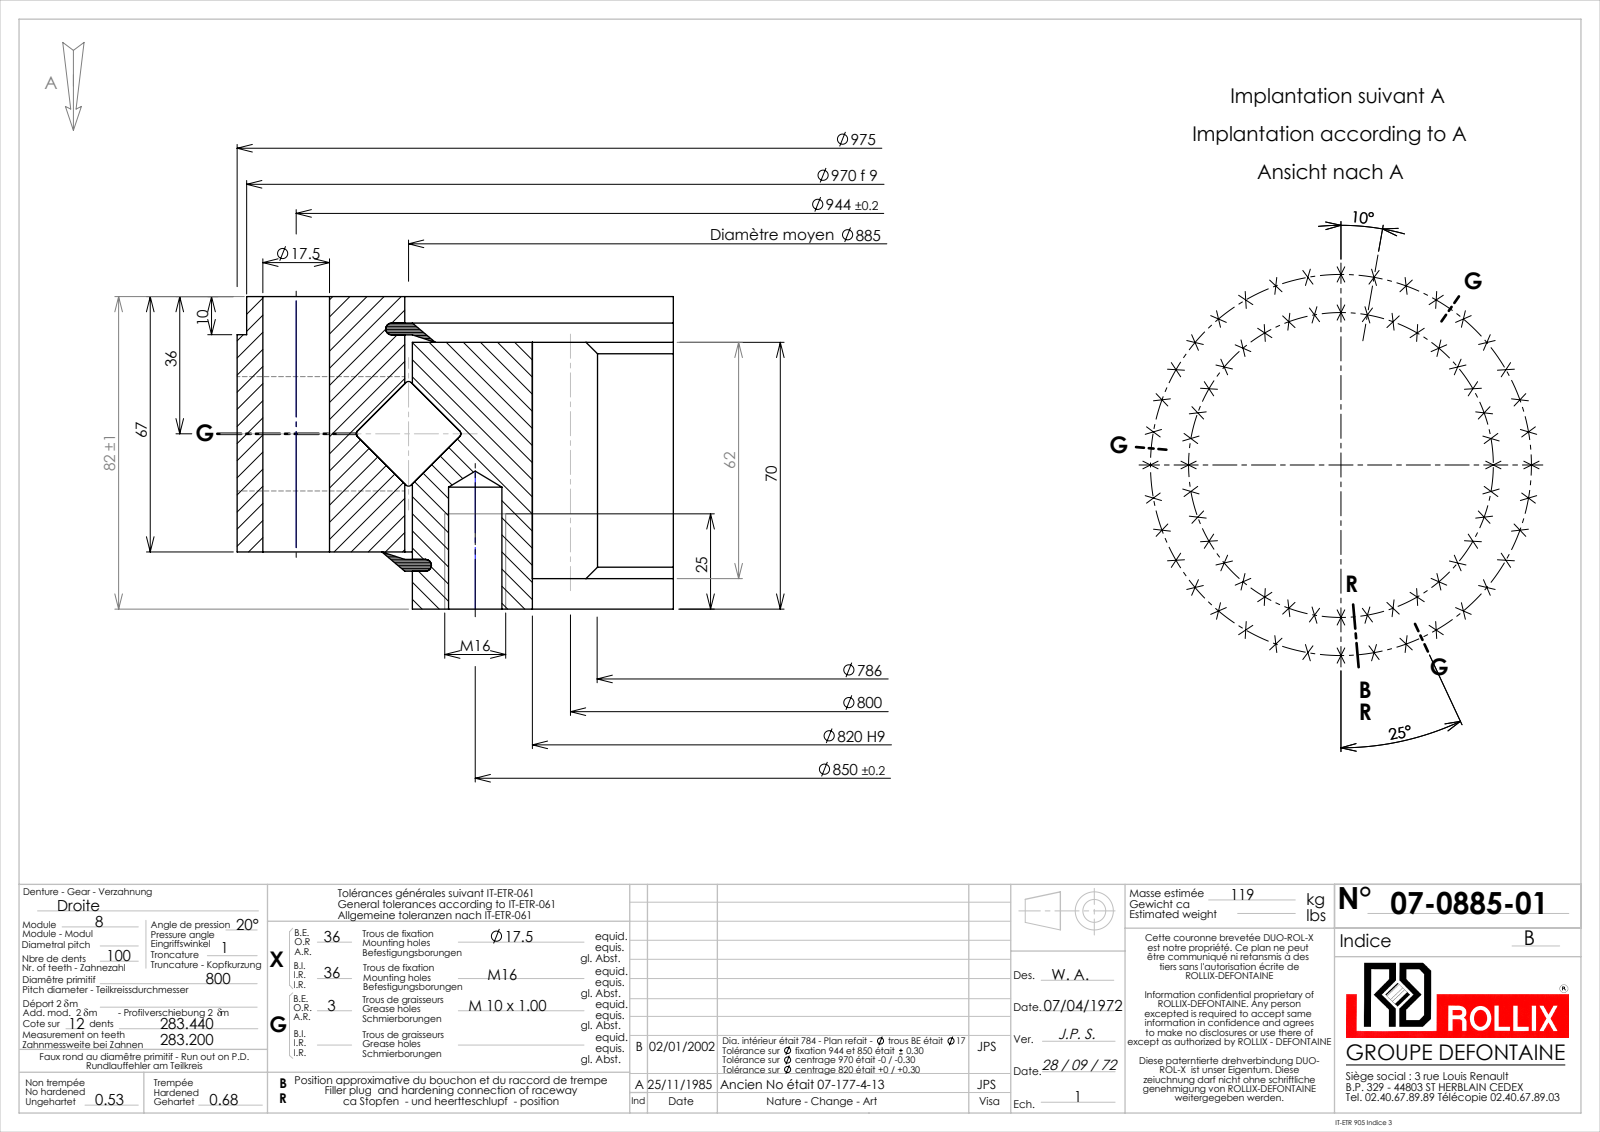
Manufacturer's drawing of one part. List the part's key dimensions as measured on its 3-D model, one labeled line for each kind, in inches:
Part name (STEP PRODUCT): 07-0885-01
STEP written by: SolidWorks 2016 (CONFIG_CONTROL_DESIGN)
Units: inches
Bodies: 5 solids, 897 faces (315 planar, 270 cylindrical, 312 other)
Overall size (bounding box): 38.386 × 38.386 × 3.228
Volume: 869.6 in³ · Surface area: 2 821 in²
Round holes (diameter × count): ⌀0.551 ×36, ⌀0.689 ×36, ⌀0.354 ×3, ⌀32.283 ×1, ⌀34.921 ×1
Round bosses / shafts (diameter × count): ⌀38.386 ×1, ⌀38.189 ×1, ⌀34.764 ×1, ⌀0.787 ×1
Partial cylindrical surfaces — rounded edges, fillets, slot ends (radius × count): R15.472 ×1
Main face-to-face distances: 2.638, 2.165, 0.472, 0.591, 2.756, 3.228, 0.199, 0.077, 2.441, 2.364
Hole centre spacings: 16.732, 5.811, 2.917, 19.194, 23.663, 30.329, 8.661, 11.446
